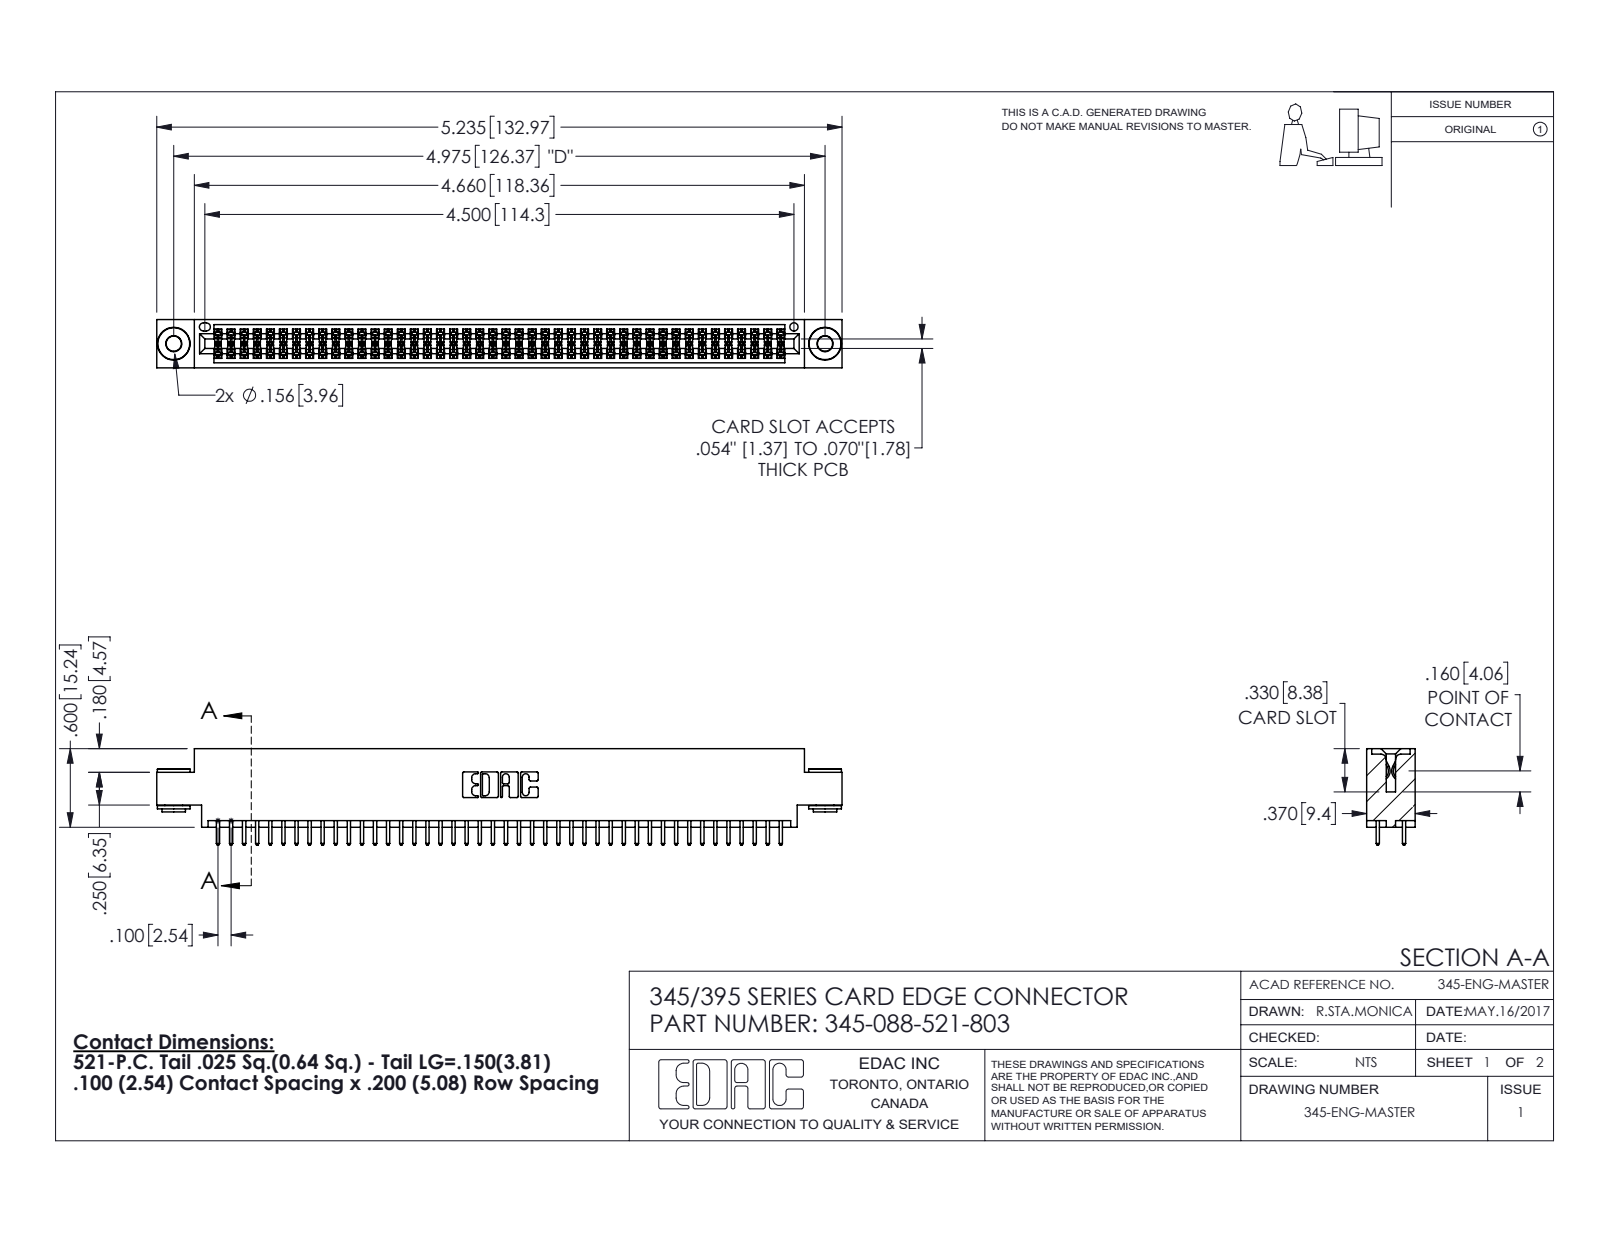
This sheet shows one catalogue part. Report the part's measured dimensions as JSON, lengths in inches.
{"part_name": "345-088-521-803; 345-250-002_345-250-002-102; 345-292-001_345-293-121; 345 Part_0.170 Offset - 0.156 Dia-TH", "step_written_by": "SolidWorks 2016 (CONFIG_CONTROL_DESIGN)", "units": "inches", "bodies": {"solids": 91, "faces": 4568, "planar": 2998, "cylindrical": 1562, "other": 8}, "overall_size": [5.235, 0.737, 0.37], "volume_in3": 0.781, "surface_area_in2": 29.58, "round_holes": [[0.116, 2], [0.156, 2], [0.064, 1]], "round_bosses_or_shafts": [[0.25, 2], [0.18, 2], [0.136, 2]], "partial_cylinders_radius": [[0.006, 132], [0.01, 88], [0.01, 22], [0.007, 6], [0.031, 6], [0.026, 3], [0.014, 2], [0.019, 2]], "face_to_face_distances": [0.072, 0.298, 0.37, 0.2, 0.098, 0.272, 0.025, 0.225, 0.175, 0.149], "hole_center_spacings": [0.27, 4.739, 4.975]}
